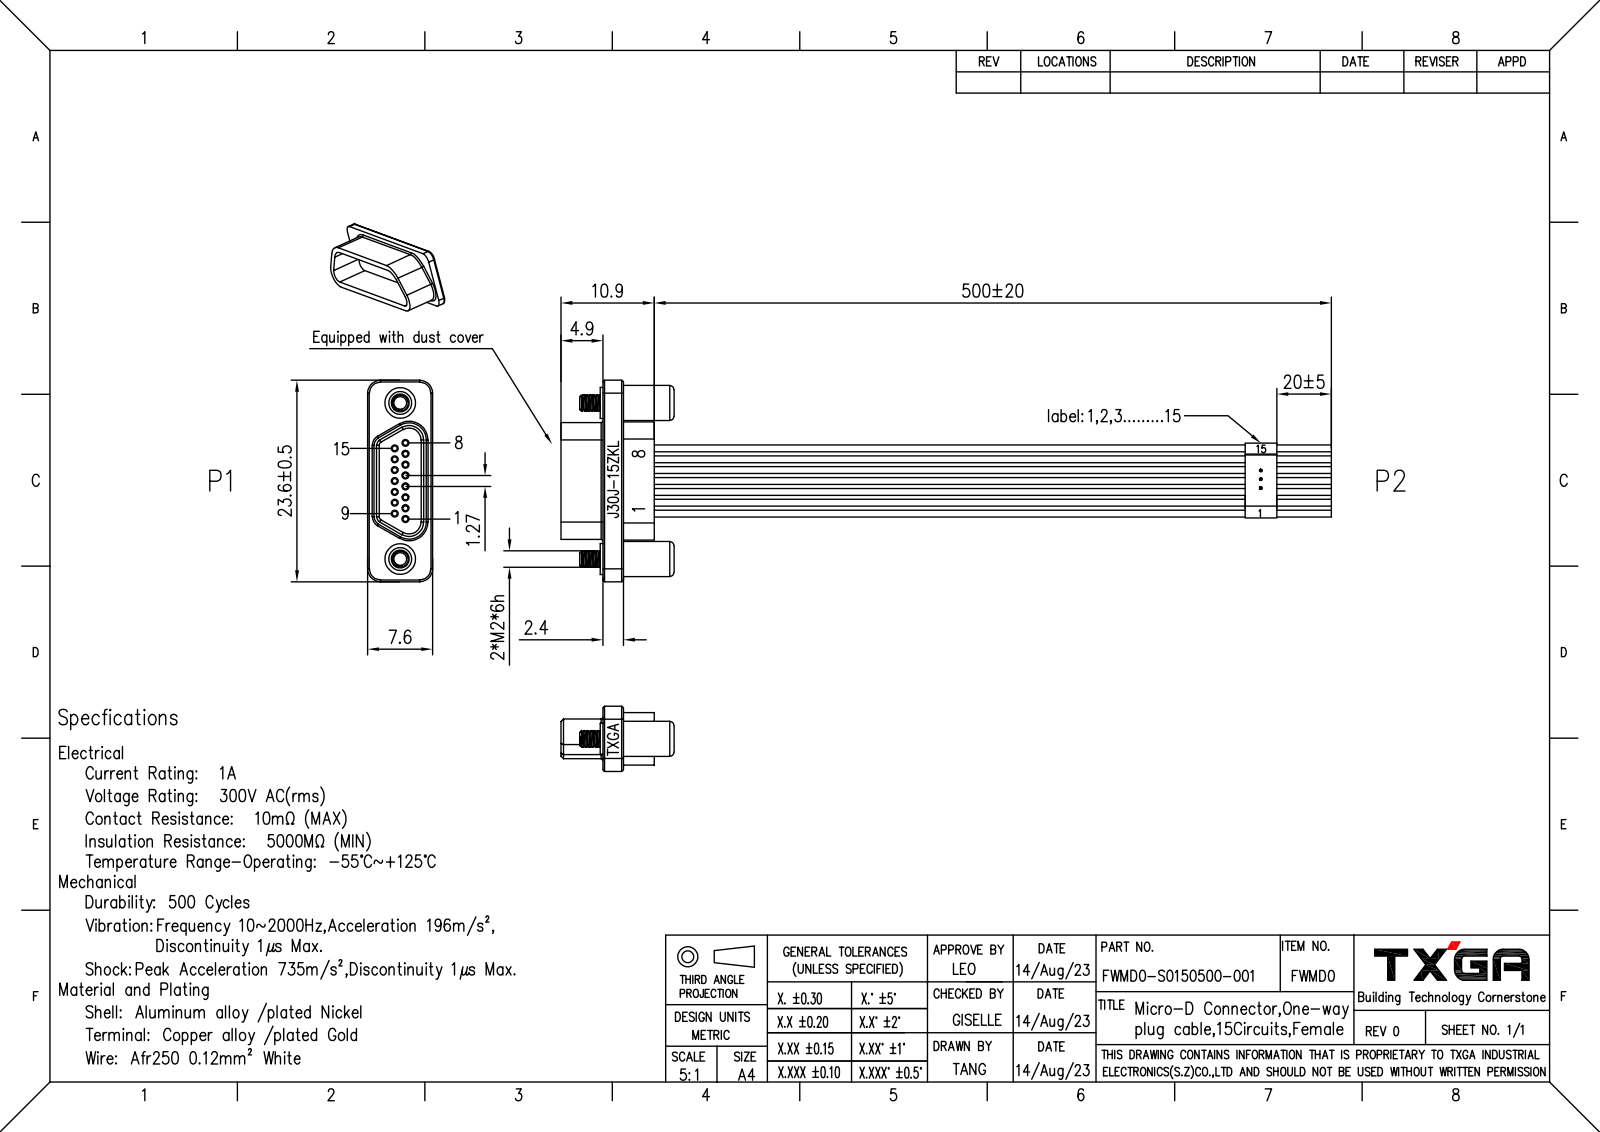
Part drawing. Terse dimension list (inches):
name: 1-1; 2-1; 3-1; LUOSISHELL (+4 more)
written by: PRO/ENGINEER BY PARAMETRIC TECHNOLOGY CORPORATION, 2010280 (CONFIG_CONTROL_DESIGN)
unit: in
bodies: 35 solids, 716 faces (352 planar, 280 cylindrical, 84 other)
size: 3.579 × 0.925 × 0.299
volume: 0.099 in³; area: 8.634 in²
holes: 15× ⌀0.024, 15× ⌀0.031, 2× ⌀0.083, 2× ⌀0.11, 2× ⌀0.126, 2× ⌀0.138
bosses: 17× ⌀0.031, 2× ⌀0.161, 2× ⌀0.142, 2× ⌀0.128, 2× ⌀0.075
rounds: 32× R0.008, 10× R0.055, 6× R0.039, 4× R0.016, 4× R0.059, 4× R0.079, 2× R0.031, 2× R0.063
face distances: 0.024, 0.193, 0.039, 0.429, 0.24, 0.39, 0.053, 0.246, 0.014, 0.037
hole spacings: 0.056, 0.05, 0.1, 0.15, 0.09, 0.091, 0.135, 0.2
